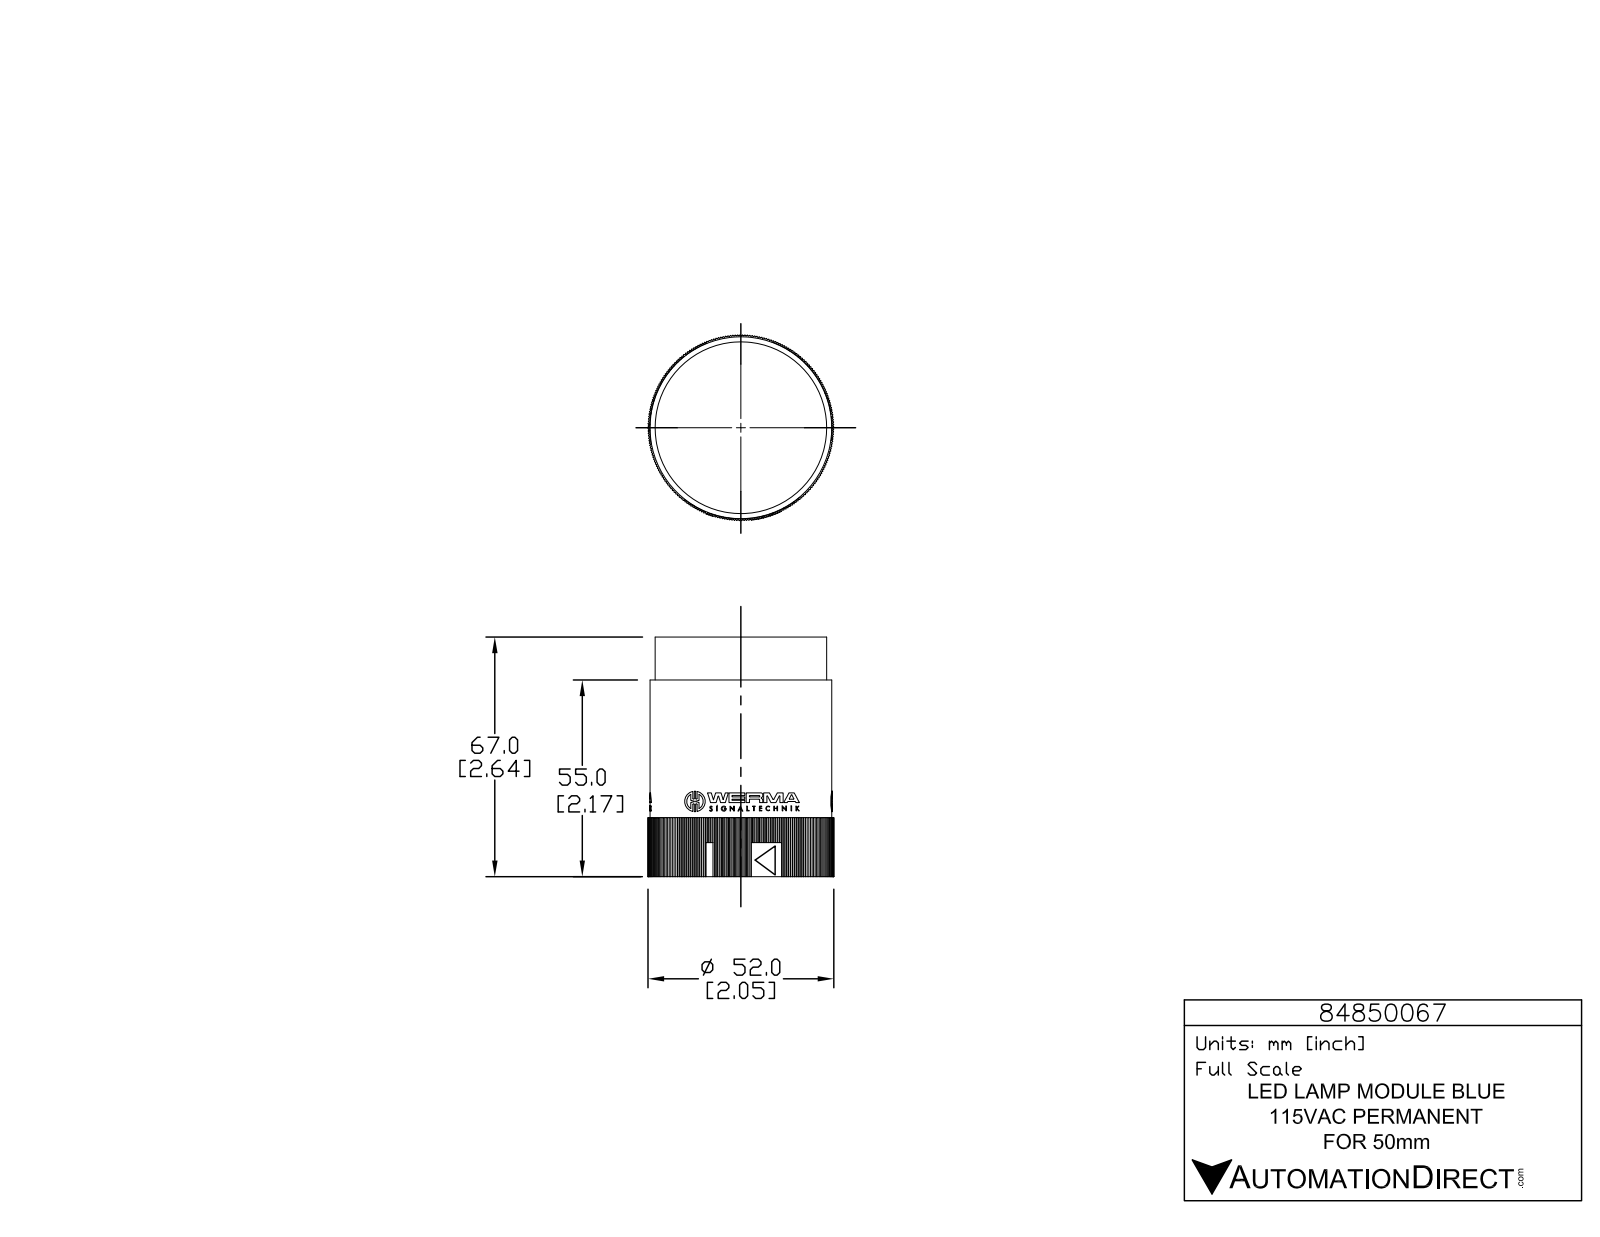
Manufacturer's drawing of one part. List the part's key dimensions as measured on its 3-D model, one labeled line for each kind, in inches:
Part name (STEP PRODUCT): 84850067
STEP written by: SolidWorks 2015 (AUTOMOTIVE_DESIGN)
Units: inches
Bodies: 1 solid, 1265 faces (1020 planar, 245 cylindrical, 0 other)
Overall size (bounding box): 2.638 × 2.047 × 2.047
Volume: 6.873 in³ · Surface area: 27.62 in²
Round holes (diameter × count): ⌀0.039 ×3, ⌀1.898 ×1
Round bosses / shafts (diameter × count): ⌀0.226 ×3, ⌀0.056 ×3, ⌀2.002 ×1, ⌀1.89 ×1
Partial cylindrical surfaces — rounded edges, fillets, slot ends (radius × count): R0.008 ×6, R0.008 ×6, R0.008 ×6, R0.131 ×6, R0.004 ×3, R0.005 ×3, R0.008 ×3, R0.008 ×3
Main face-to-face distances: 2.165, 1.428, 1.429, 1.429, 0.472, 2.638, 1.428, 1.428, 1.693, 1.988
